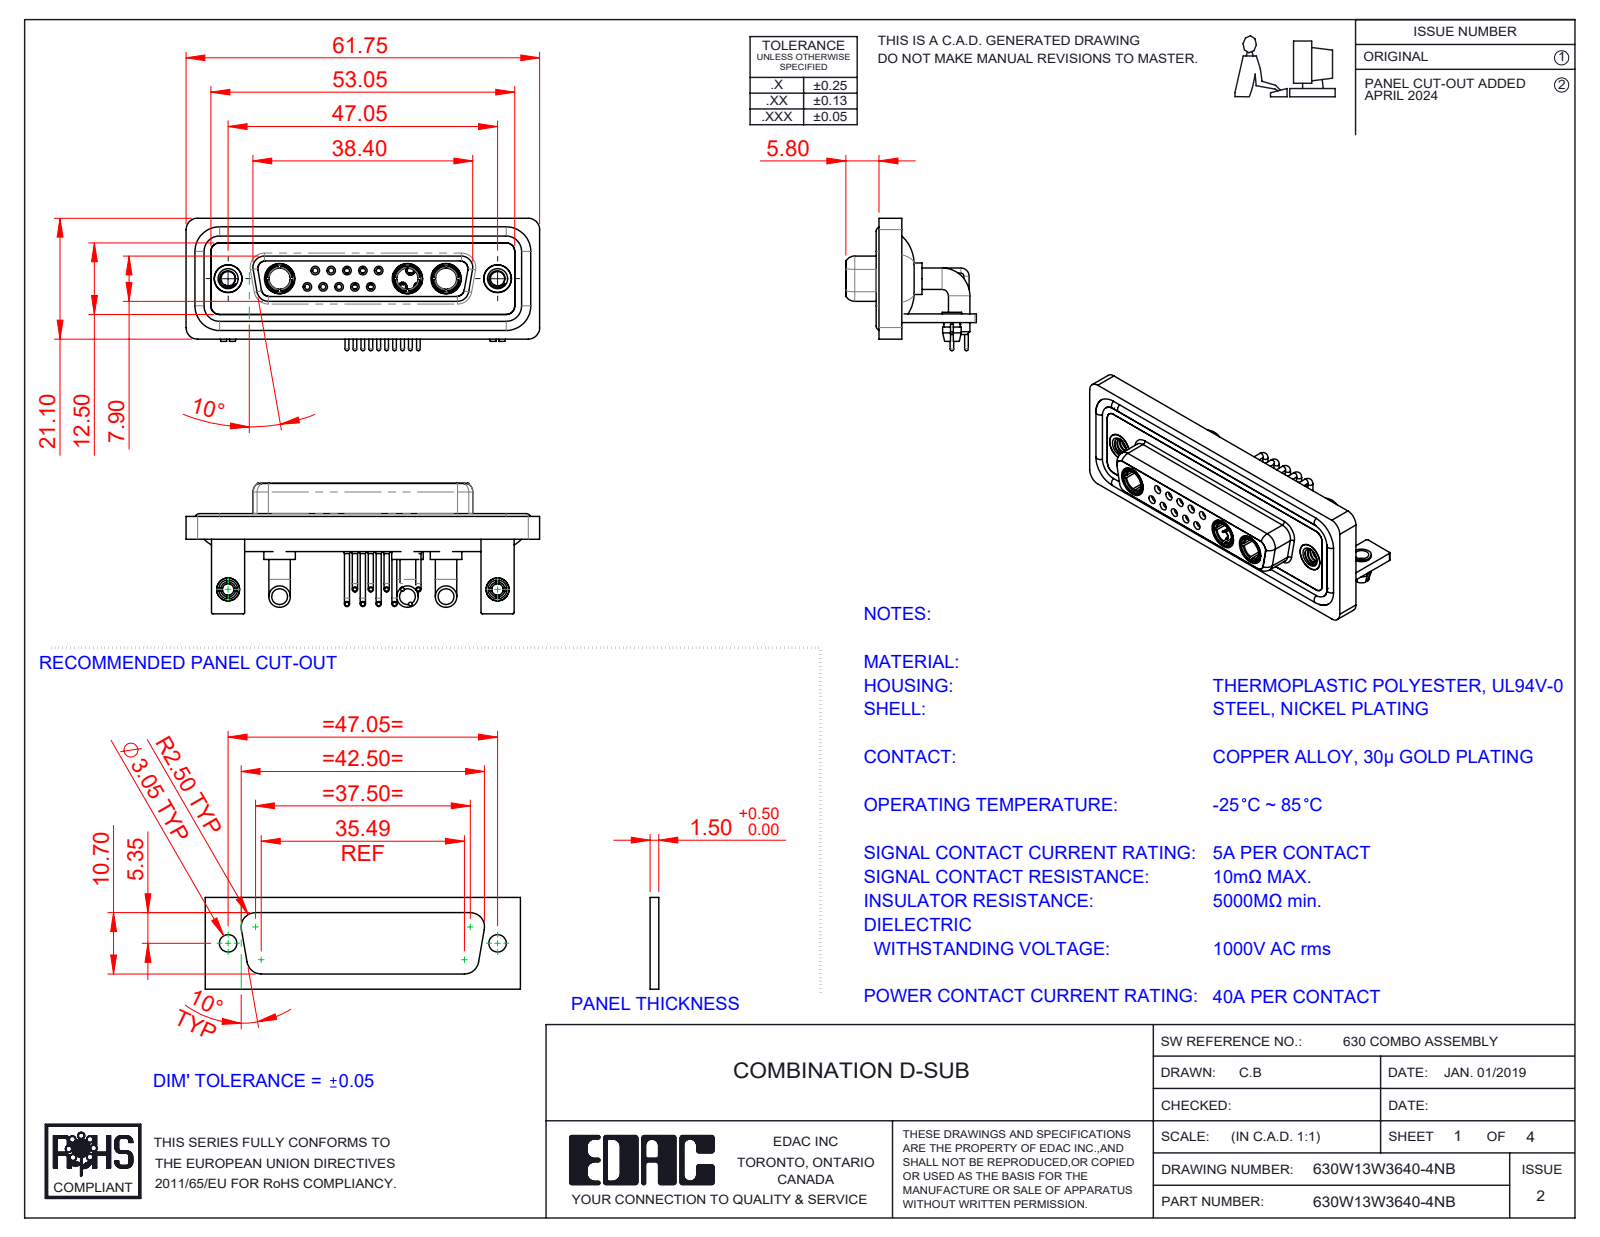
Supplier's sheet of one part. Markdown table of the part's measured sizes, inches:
| quantity | value |
| --- | --- |
| part name | 630Combo Shell Rear_25 Contacts; 630Combo Contact Row 2_50 Contacts; 630Combo Board Lock_50 Contacts; 630W13W3640-4NB (+7 more) |
| STEP written by | SolidWorks 2023 (CONFIG_CONTROL_DESIGN) |
| units | inches |
| bodies | 27 solids, 1284 faces (410 planar, 547 cylindrical, 327 other) |
| overall size | 2.431 × 0.91 × 0.898 |
| volume | 0.554 in³ |
| surface area | 23.83 in² |
| round holes (diameter × count) | 0.079 × 12, 0.035 × 10, 0.043 × 10, 0.059 × 10, 0.063 × 5, 0.067 × 5, 0.191 × 5, 0.098 × 4, 0.146 × 3, 0.209 × 3, 0.126 × 2, 0.157 × 2 |
| round bosses / shafts (diameter × count) | 0.035 × 15, 0.063 × 12, 0.026 × 10, 0.148 × 6, 0.079 × 5, 0.059 × 5, 0.217 × 3, 0.205 × 3 |
| partial cylindrical surfaces (radius × count) | 0.079 × 19, 0.059 × 18, 0.01 × 16, 0.053 × 8, 0.063 × 8, 0.02 × 5, 0.024 × 4, 0.026 × 4 |
| main face-to-face distances | 0.016, 0.071, 0.114, 0.146, 0.059, 0.161, 0.043, 0.055, 0.063, 0.122 |
| hole center spacings | 0.124, 0.109, 0.218, 0.198, 0.327, 0.198, 0.295, 0.436 |
